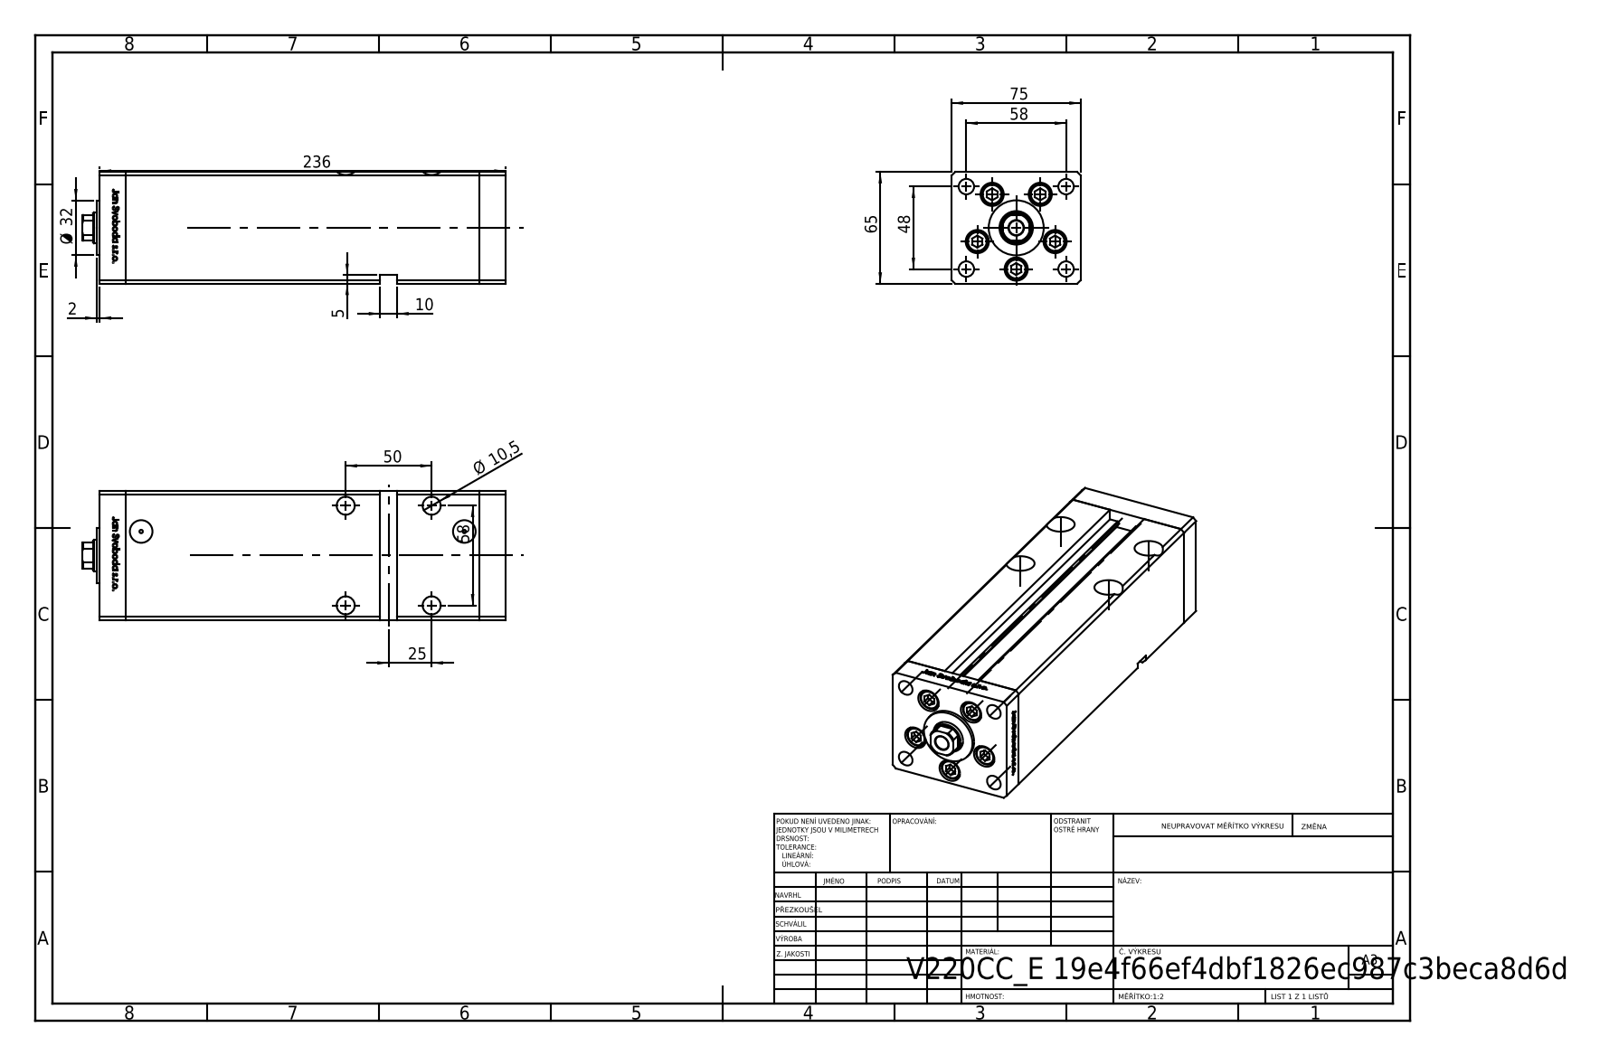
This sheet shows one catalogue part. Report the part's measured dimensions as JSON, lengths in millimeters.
{"part_name": "V220C BACK_E; V220C_E MIDDLE; ALLEN BOLT; V220C_FRONT_E (+1 more)", "step_written_by": "SolidWorks 2019 (CONFIG_CONTROL_DESIGN)", "units": "millimeters", "bodies": {"solids": 14, "faces": 1212, "planar": 473, "cylindrical": 165, "other": 574}, "overall_size": [246, 75, 65], "volume_mm3": 975804, "surface_area_mm2": 169473, "round_holes": [[9, 9], [13.5, 5], [10.5, 4], [16.5, 4], [2, 2], [13.16, 2], [8.5, 1], [18, 1], [19.5, 1]], "round_bosses_or_shafts": [[12.5, 5], [8, 5], [32, 1]], "partial_cylinders_radius": [[0.93, 2], [8.5, 1]], "face_to_face_distances": [75, 65, 15, 206, 221, 236, 54.5, 10.5, 26.25, 48.75], "hole_center_spacings": [24, 37.64, 58, 15.67, 17.22, 27.71, 28.83, 29]}
